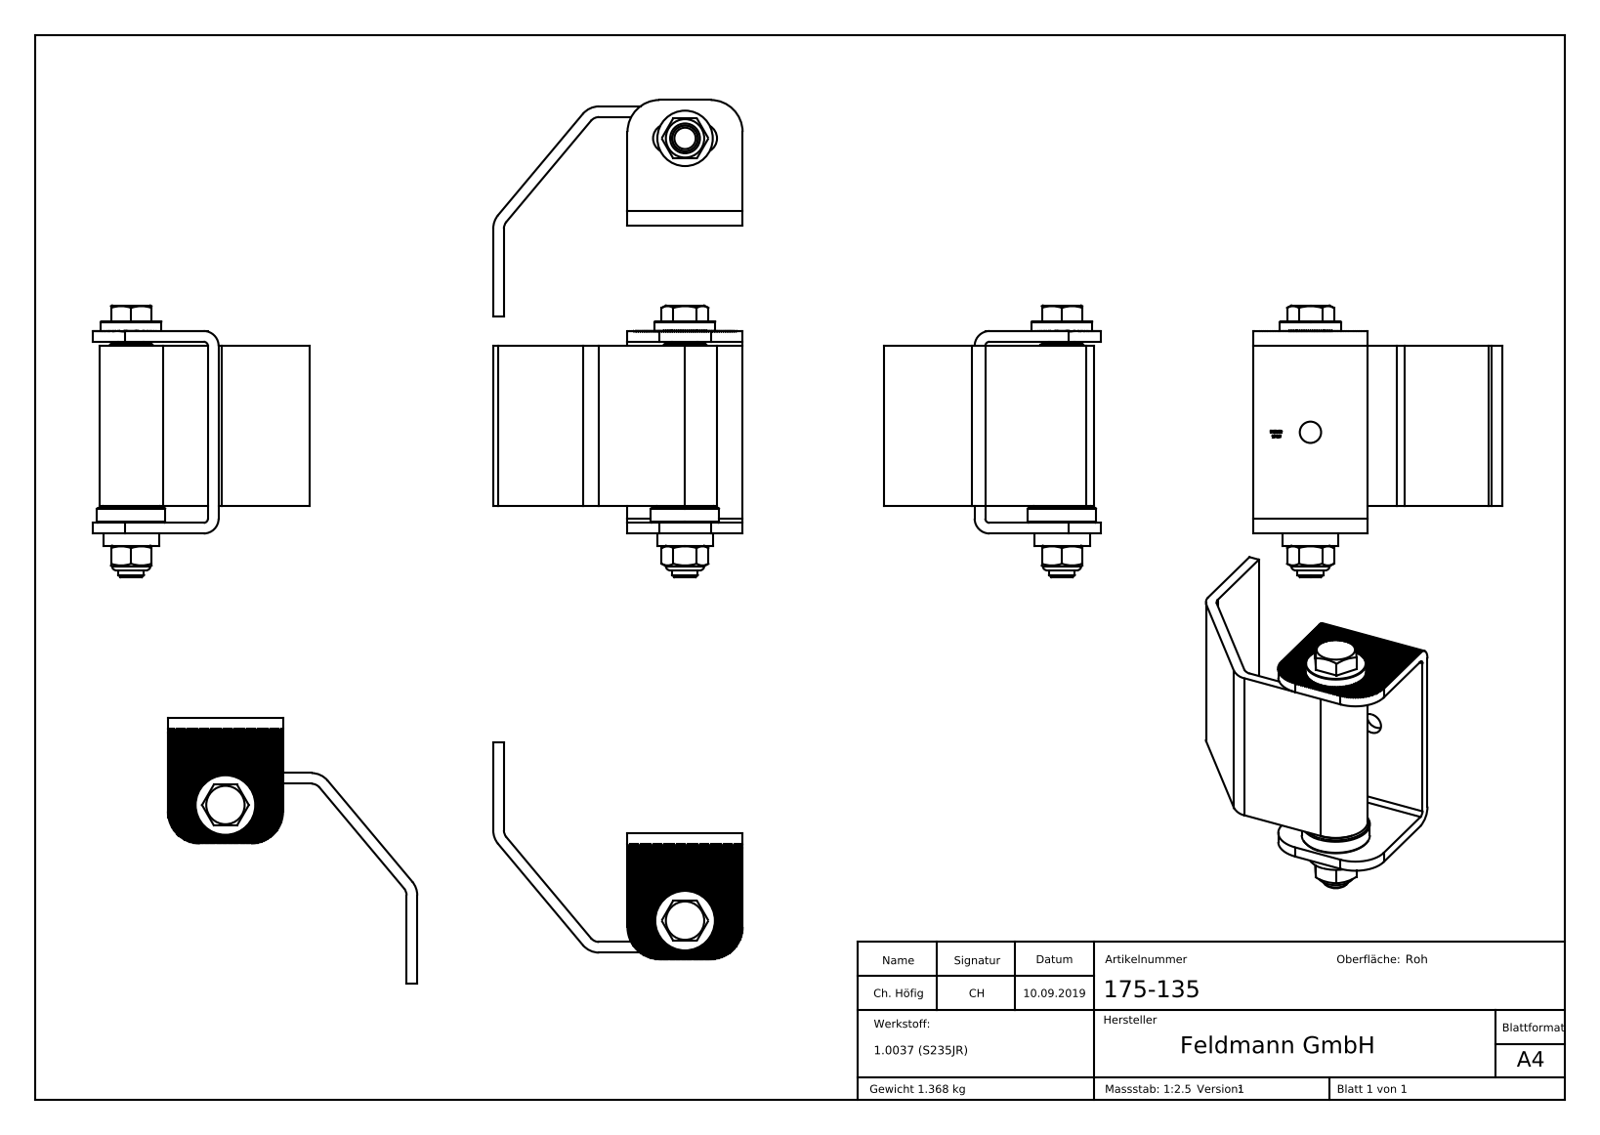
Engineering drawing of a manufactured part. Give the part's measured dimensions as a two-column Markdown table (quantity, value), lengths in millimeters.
| quantity | value |
| --- | --- |
| part name | 175-XX Teil4_175-135 Teil4; 175-XX Teil8_175-135 Teil8; 175-XX Teil6_175-135 Teil6; 175-XX Teil3_175-135 Teil3 (+5 more) |
| STEP written by | SolidWorks 2015 (CONFIG_CONTROL_DESIGN) |
| units | millimeters |
| bodies | 9 solids, 693 faces (535 planar, 46 cylindrical, 112 other) |
| overall size | 127.5 × 117 × 101.75 |
| volume | 175 348 mm³ |
| surface area | 81 364 mm² |
| round holes (diameter × count) | 10 × 1, 10.2 × 1, 12.2 × 1, 12.65 × 1, 12.8 × 1, 20.2 × 1 |
| round bosses / shafts (diameter × count) | 32 × 1, 30 × 1, 28.5 × 1, 27.2 × 1, 26 × 1, 20 × 1, 12 × 1 |
| partial cylindrical surfaces (radius × count) | 2 × 2, 5 × 2, 6.75 × 2, 7 × 2, 10 × 2, 15 × 2 |
| main face-to-face distances | 5, 51, 90, 46, 56, 85, 77, 95, 8, 13 |
